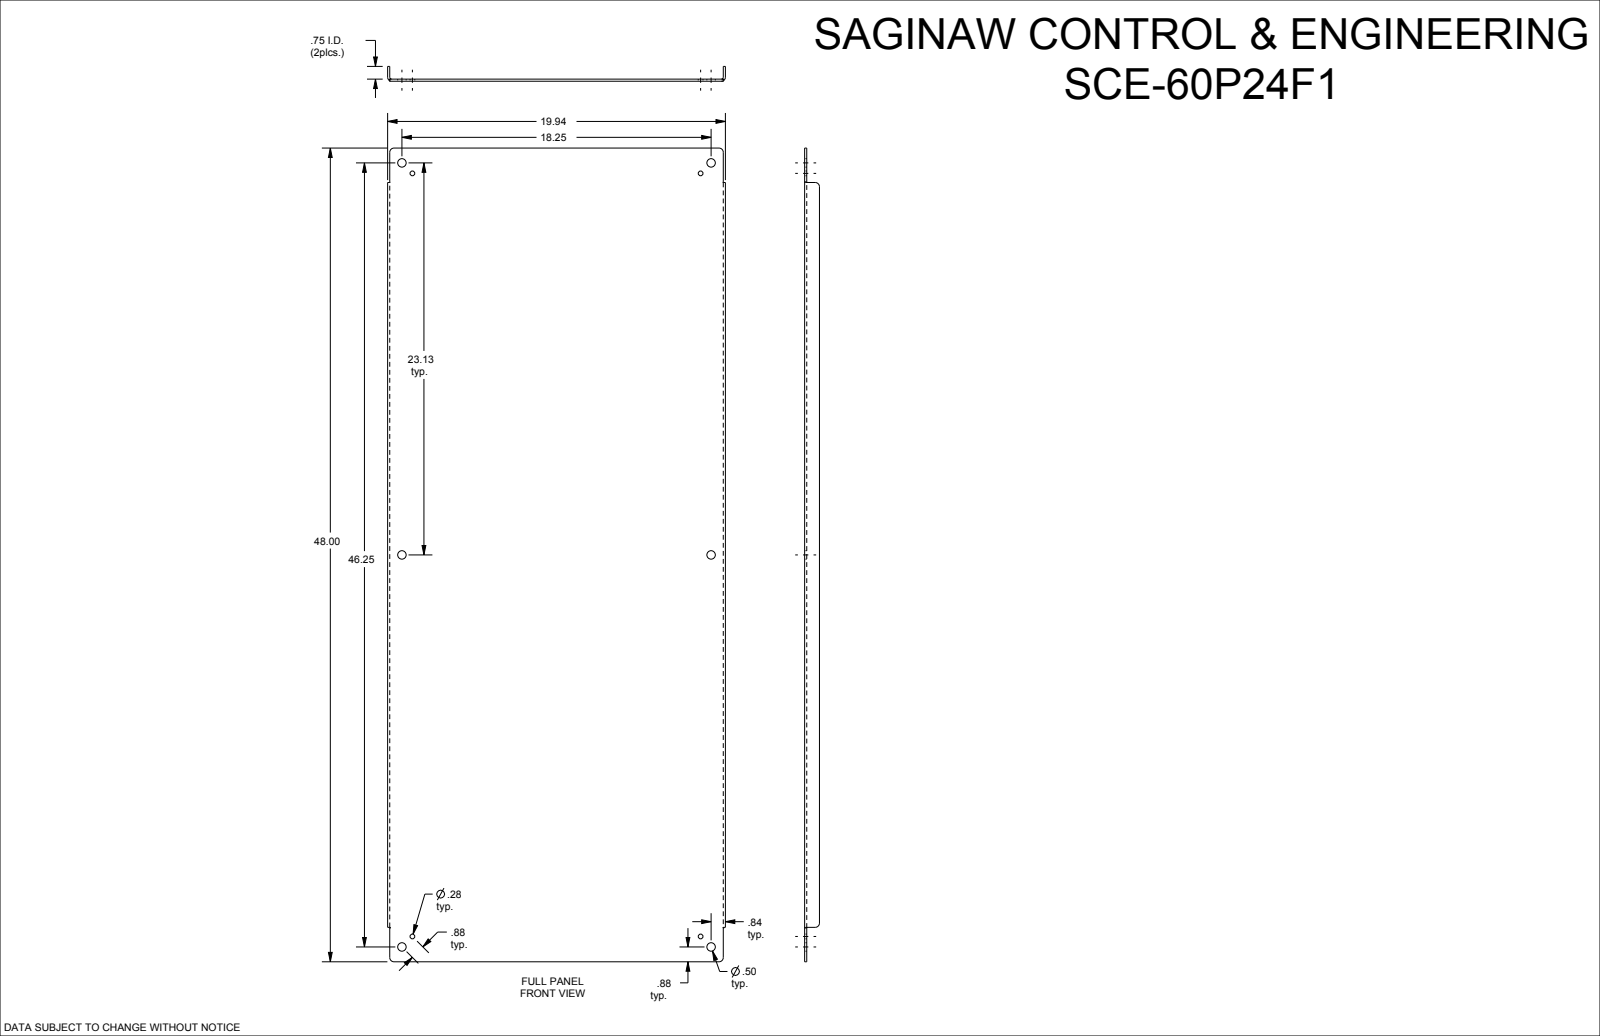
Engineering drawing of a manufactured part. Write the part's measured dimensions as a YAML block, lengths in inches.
part_name: "SCE-60P24F1"
step_written_by: "SolidWorks 2019 (CONFIG_CONTROL_DESIGN)"
units: inches
bodies: {solids: 1, faces: 52, planar: 18, cylindrical: 22, other: 12}
overall_size: [48, 19.938, 0.875]
volume: 126.7
surface_area: 2046
round_holes:
  - {diameter: 0.5, count: 6}
  - {diameter: 0.281, count: 4}
partial_cylinders:
  - {radius: 0.25, count: 6}
  - {radius: 0.112, count: 2}
  - {radius: 0.237, count: 2}
face_to_face_distances: [0.125, 0.125, 19.813, 19.687, 19.938, 0.75, 0.875, 48, 2.031, 45.969]
hole_center_spacings: [0.875, 17.642, 22.515, 23.125, 28.59, 29.459, 45.636, 48.919]
